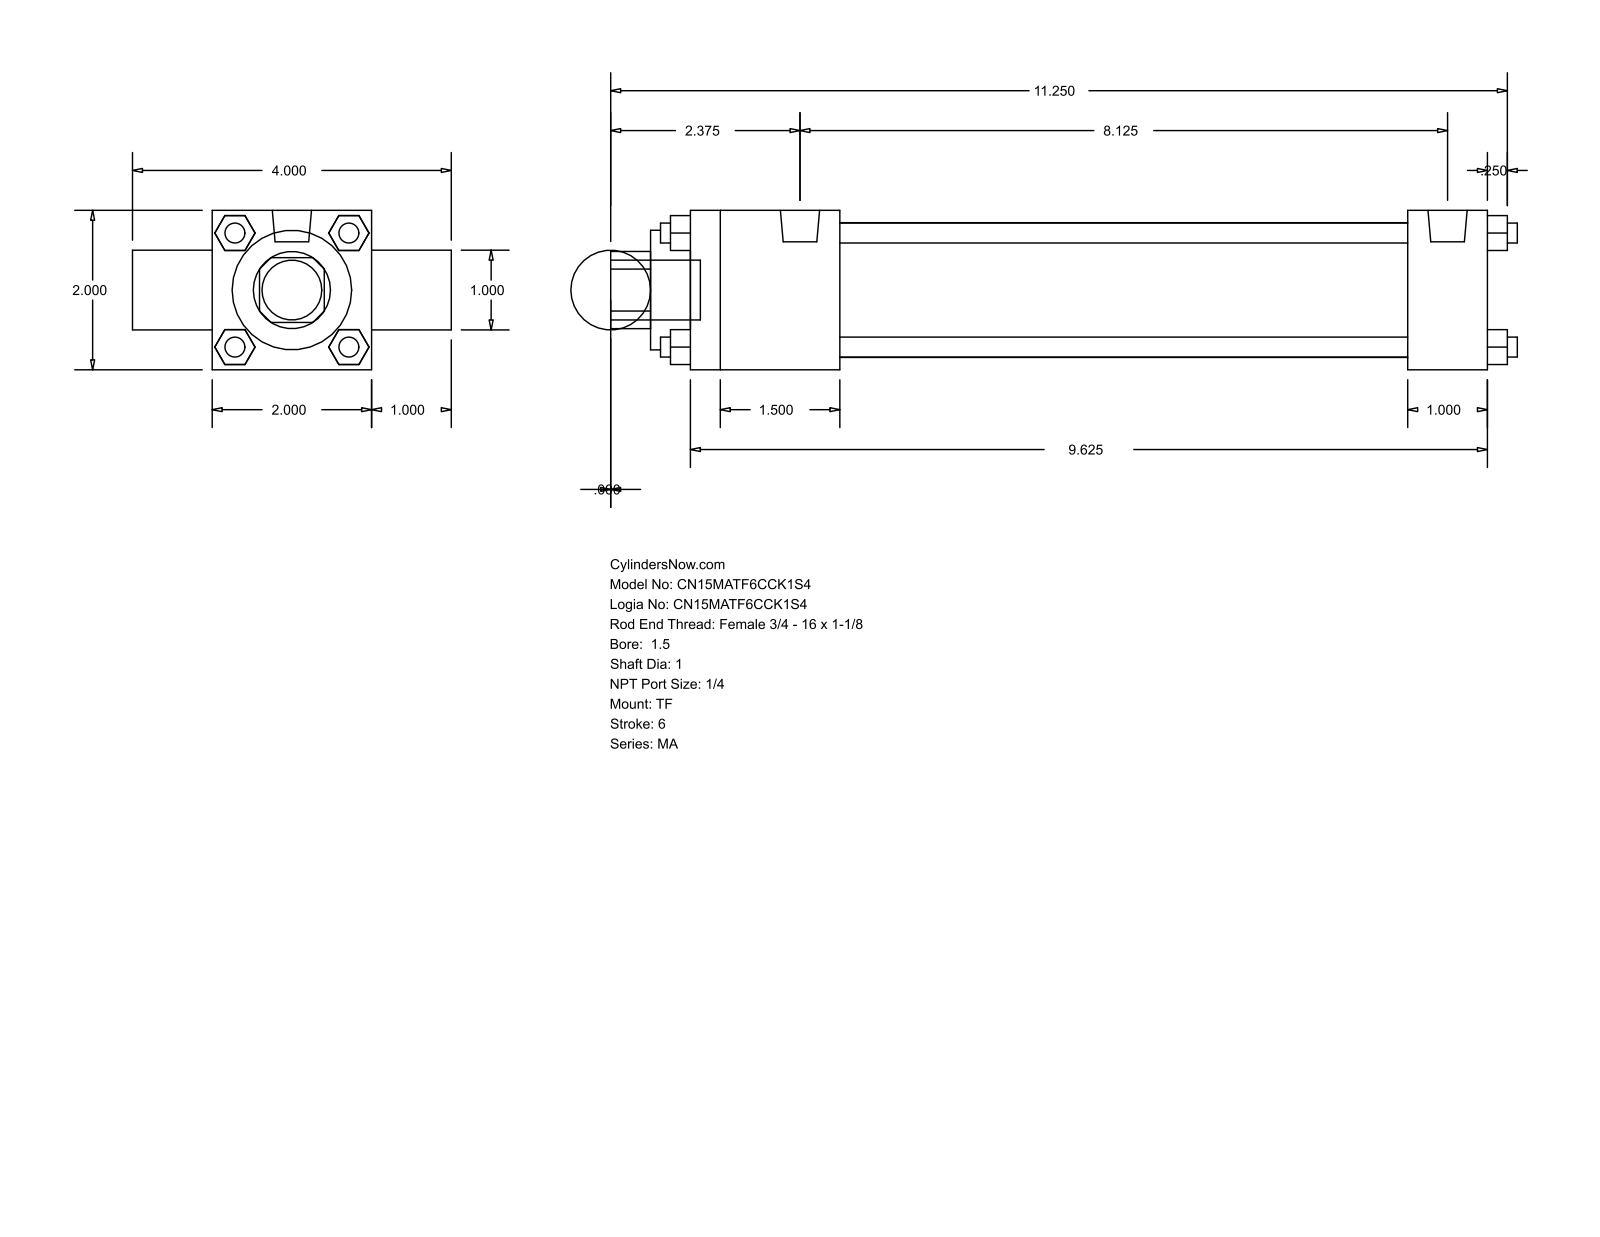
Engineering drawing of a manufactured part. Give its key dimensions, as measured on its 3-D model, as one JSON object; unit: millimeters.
{"part_name": "MA_TF__0150_1", "step_written_by": "GSSL Pune (CONFIG_CONTROL_DESIGN)", "units": "millimeters", "bodies": {"solids": 0, "faces": 120, "planar": 92, "cylindrical": 28, "other": 0}, "overall_size": [288.93, 101.6, 50.8], "round_holes": [[25.4, 2], [38.1, 1], [42.93, 1]], "round_bosses_or_shafts": [[6.35, 4], [7.94, 3], [12.49, 2], [19.05, 1]], "partial_cylinders_radius": [[12.29, 1]], "face_to_face_distances": [50.8, 25.4, 254, 76.2, 6.35, 47.63, 228.6, 180.97, 206.37, 266.7]}
